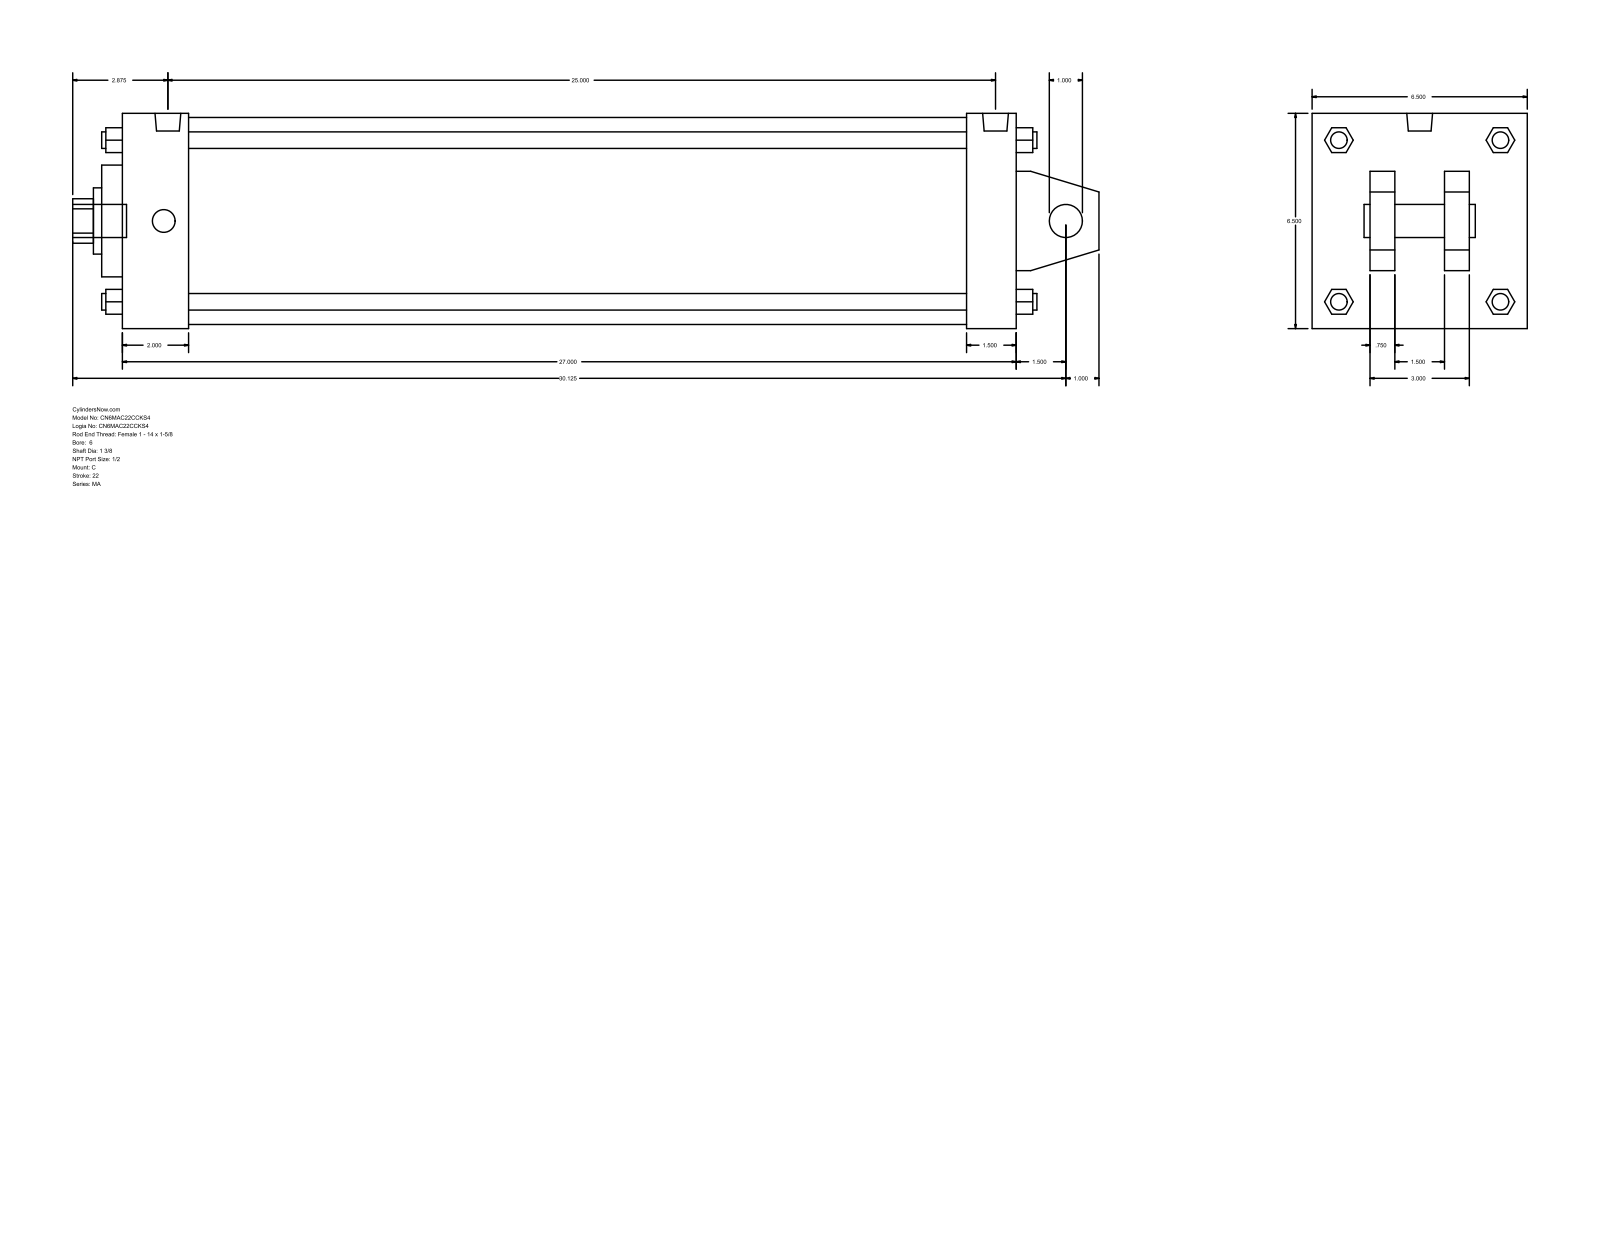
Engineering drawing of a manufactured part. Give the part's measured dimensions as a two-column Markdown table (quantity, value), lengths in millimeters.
| quantity | value |
| --- | --- |
| part name | MA_C__0600_1.375 |
| STEP written by | GSSL Pune (CONFIG_CONTROL_DESIGN) |
| units | millimeters |
| bodies | 0 solids, 141 faces (109 planar, 32 cylindrical, 0 other) |
| overall size | 787.4 × 165.1 × 165.1 |
| round holes (diameter × count) | 25.4 × 1, 34.92 × 1, 50.8 × 1, 85.72 × 1, 158.75 × 1 |
| round bosses / shafts (diameter × count) | 17.46 × 4, 12.7 × 4, 19.77 × 2, 25.4 × 1 |
| partial cylindrical surfaces (radius × count) | 17.06 × 1 |
| main face-to-face distances | 165.1, 685.8, 38.1, 19.05, 63.5, 101.6, 50.8, 44.45, 120.65, 647.7 |
